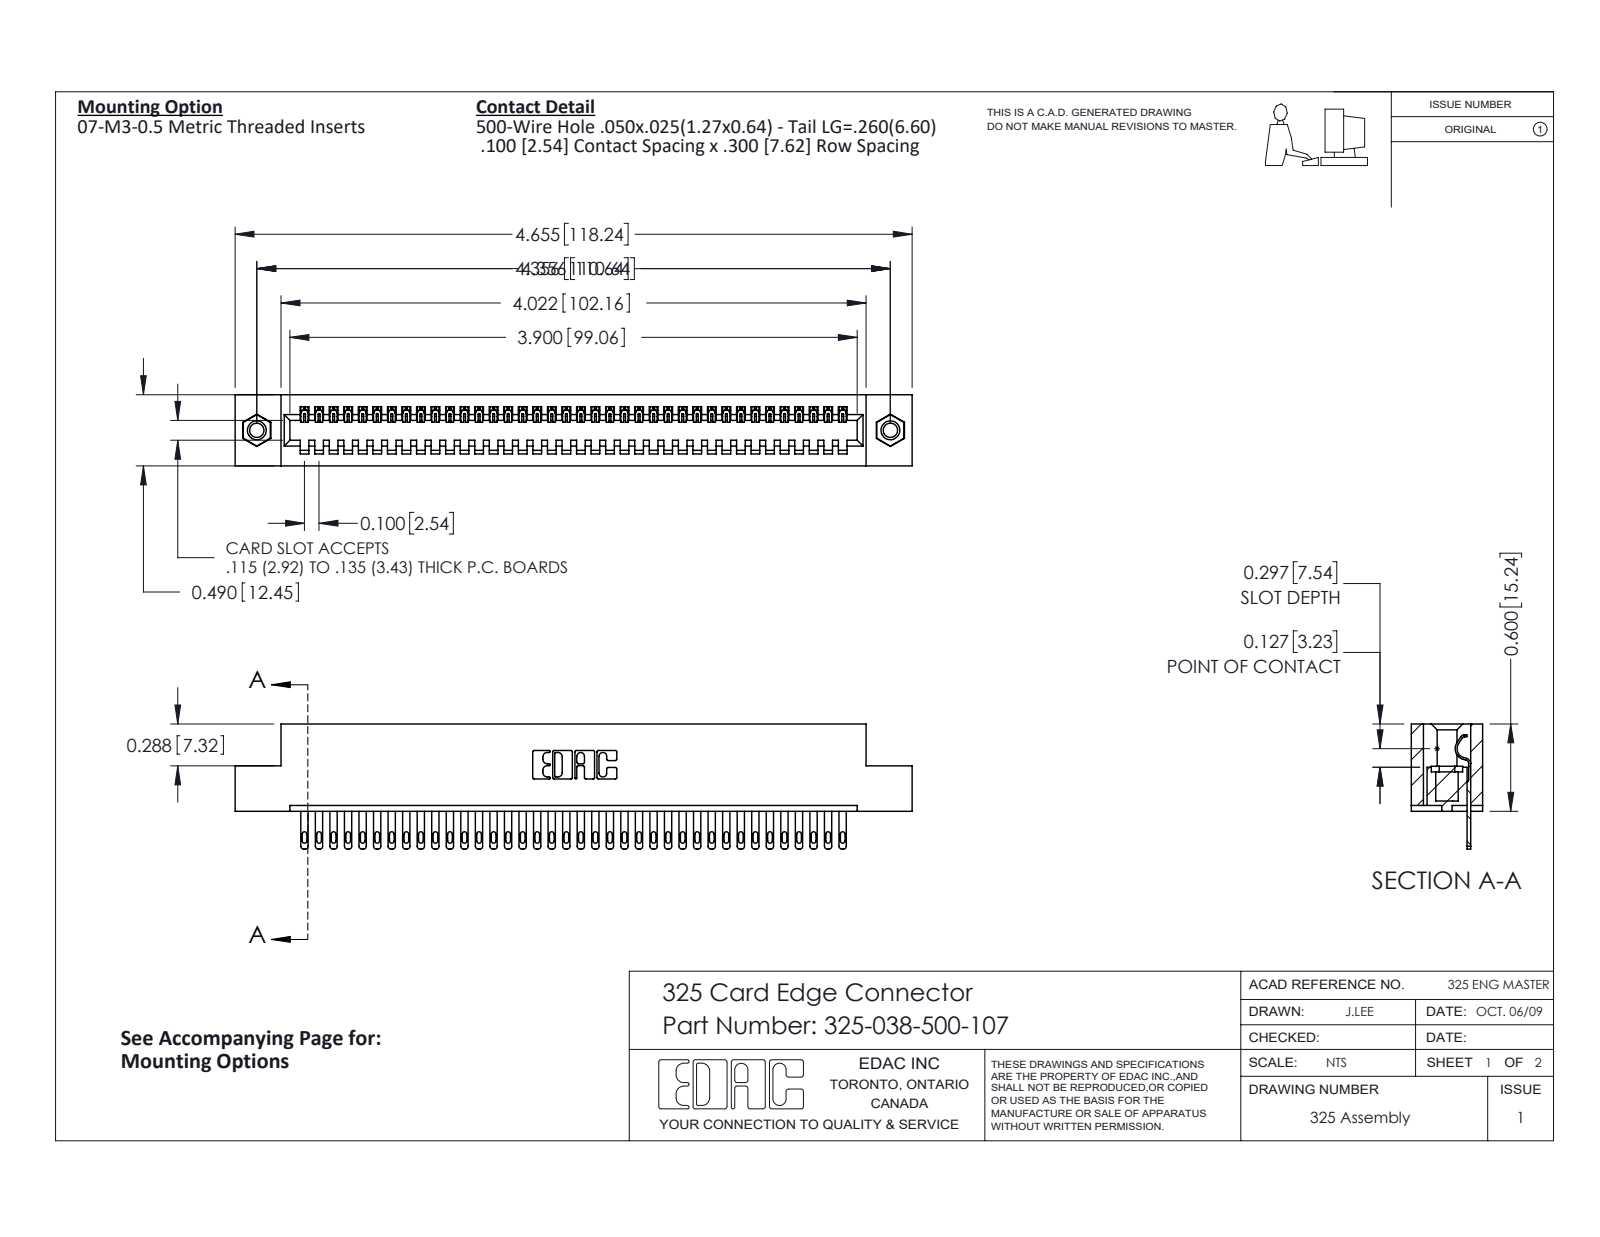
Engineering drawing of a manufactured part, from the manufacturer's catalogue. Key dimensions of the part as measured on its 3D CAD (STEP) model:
Part name (STEP PRODUCT): 325 Part_TI; 325-292-001_325-293-100; 345-250-001_345-250-005-103; 325-038-500-107
STEP written by: SolidWorks 2016 (CONFIG_CONTROL_DESIGN)
Units: inches
Bodies: 41 solids, 2226 faces (1470 planar, 740 cylindrical, 16 other)
Overall size (bounding box): 4.655 × 0.86 × 0.49
Volume: 0.915 in³ · Surface area: 25.46 in²
Round holes (diameter × count): ⌀0.098 ×2, ⌀0.125 ×2, ⌀0.16 ×2
Round bosses / shafts (diameter × count): ⌀0.155 ×2
Partial cylindrical surfaces — rounded edges, fillets, slot ends (radius × count): R0.006 ×76, R0.016 ×76, R0.02 ×76, R0.01 ×22, R0.007 ×6, R0.031 ×6, R0.026 ×3, R0.014 ×1
Main face-to-face distances: 0.083, 0.407, 0.49, 0.3, 0.107, 0.383, 0.025, 0.325, 0.56, 0.263
Hole centre spacings: 4.356
